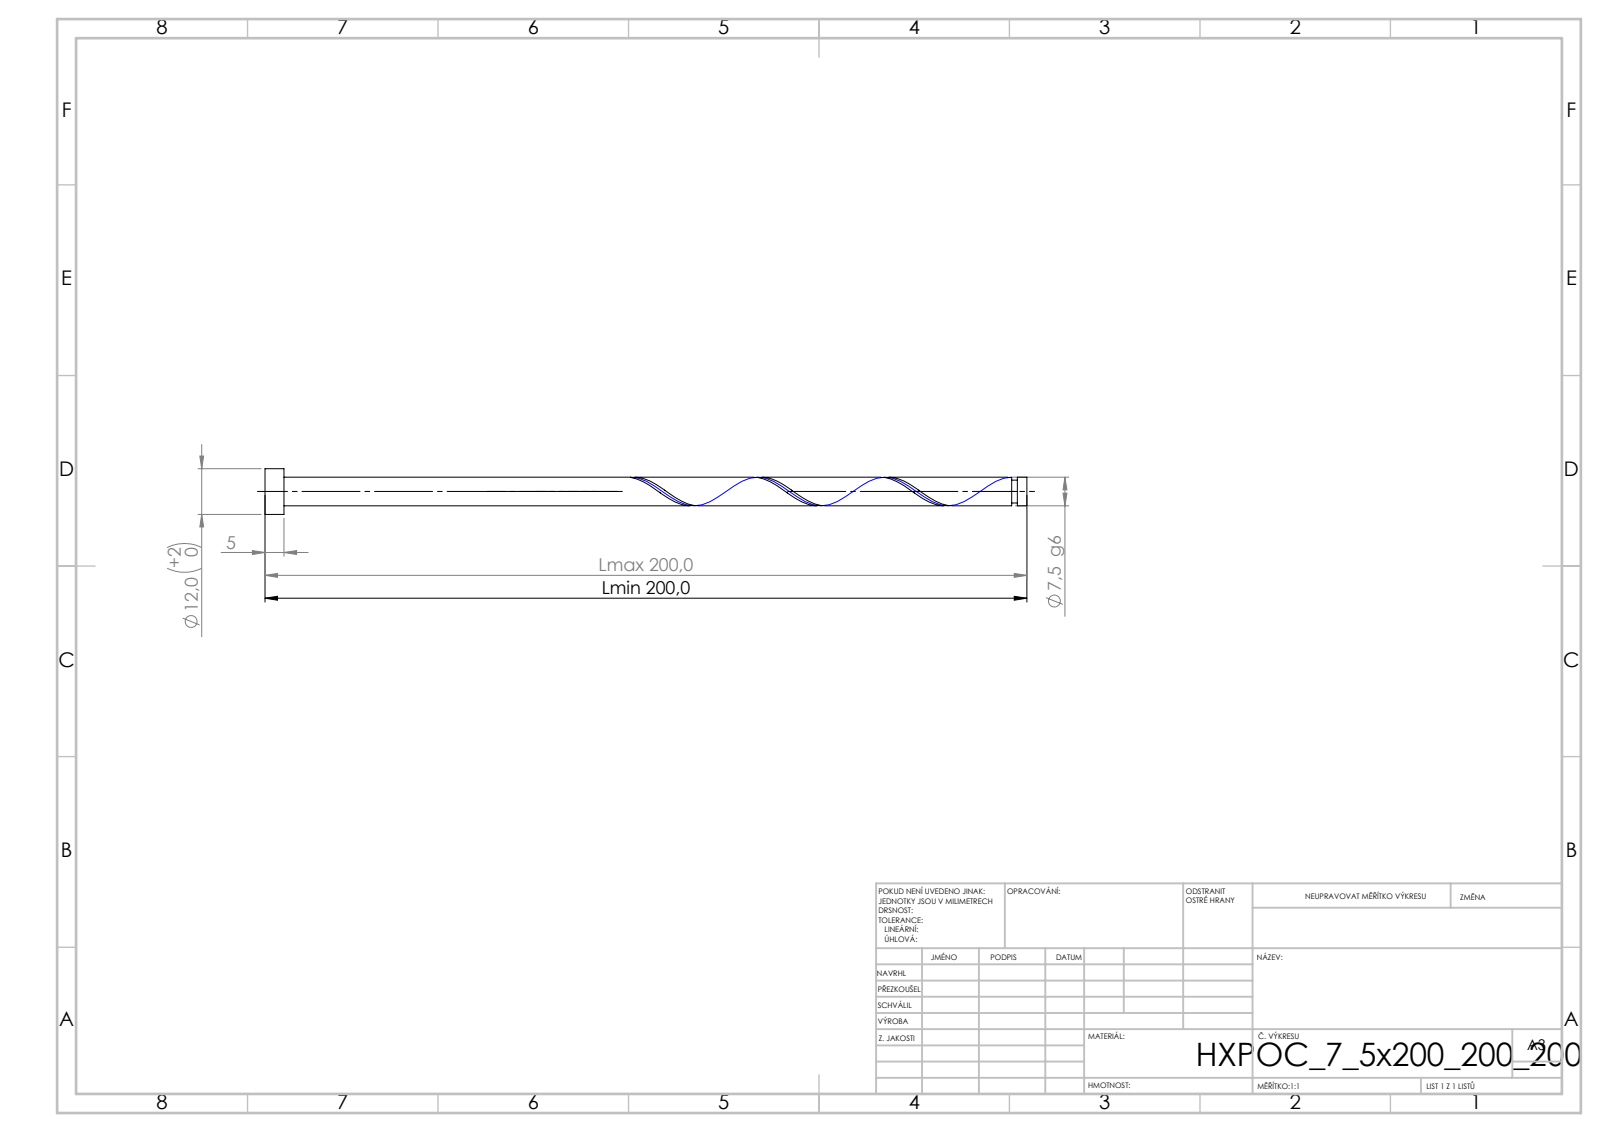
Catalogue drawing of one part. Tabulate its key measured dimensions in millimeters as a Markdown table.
| quantity | value |
| --- | --- |
| STEP written by | SolidWorks 2019 (CONFIG_CONTROL_DESIGN) |
| units | millimeters |
| bodies | 1 solid, 21 faces (6 planar, 14 cylindrical, 1 other) |
| overall size | 200 × 12 × 12 |
| volume | 9 072 mm³ |
| surface area | 5 128 mm² |
| round bosses / shafts (diameter × count) | 12 × 1, 7.5 × 1, 6 × 1 |
| main face-to-face distances | 5, 200, 195, 197.51, 192.51, 2.49, 196.01, 191.01, 1.5, 3.99 |
